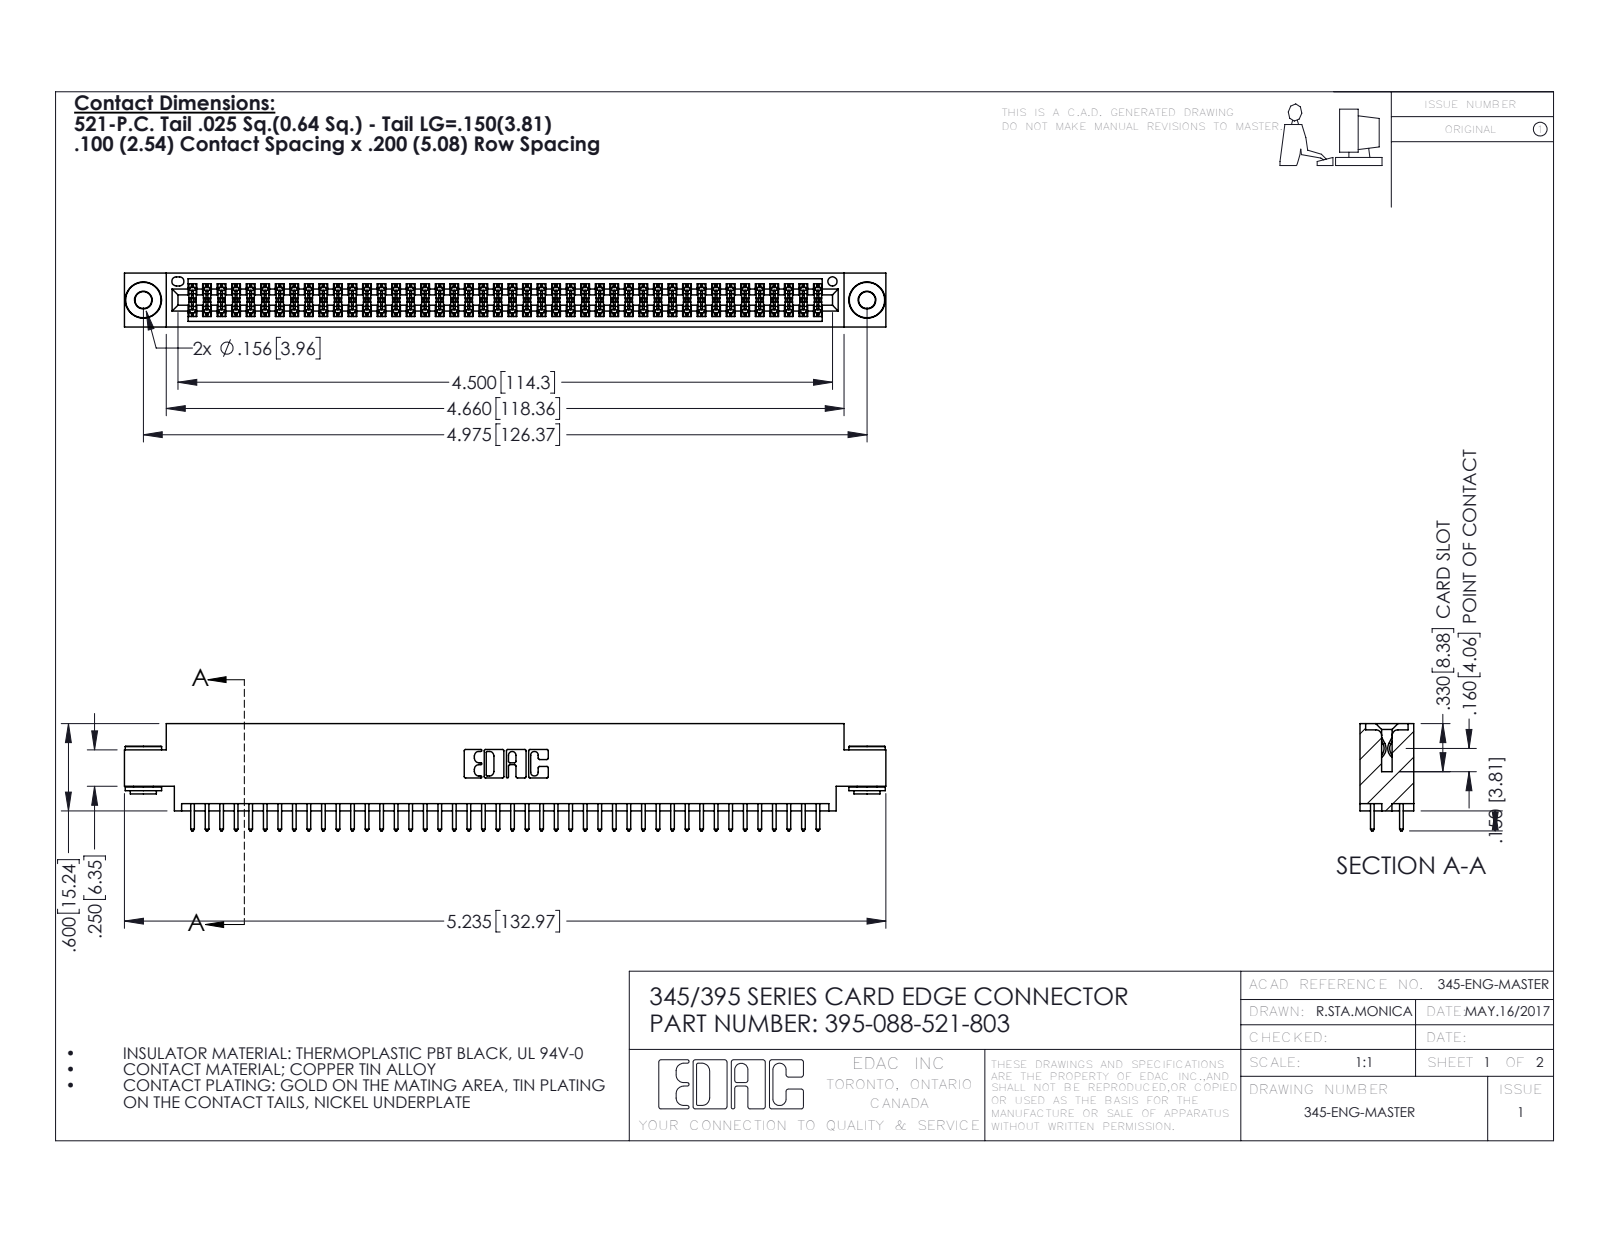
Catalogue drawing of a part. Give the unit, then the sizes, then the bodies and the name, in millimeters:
Units: millimetres
Overall size (bounding box): 133 × 18.7 × 9.4
Round holes (diameter × count): ⌀2.9 ×2, ⌀4 ×2, ⌀1.6 ×1
Round bosses / shafts (diameter × count): ⌀6.4 ×2, ⌀4.6 ×2, ⌀3.5 ×2
Partial cylindrical surfaces — rounded edges, fillets, slot ends (radius × count): R0.2 ×132, R0.3 ×88, R0.3 ×22, R0.2 ×6, R0.8 ×6, R0.7 ×3, R0.4 ×2, R0.5 ×2
Main face-to-face distances: 1.8, 7.6, 9.4, 5.1, 2.5, 6.9, 0.6, 5.7, 4.4, 3.8
Hole centre spacings: 6.9, 120.4, 126.4
Volume: 12 800 mm³ · Surface area: 19 080 mm²
Bodies: 91 solids, 4568 faces (2998 planar, 1562 cylindrical, 8 other)
Part name (STEP PRODUCT): 345-292-001_345-293-121; 395-088-521-803; 345 Part_0.170 Offset - 0.156 Dia-TH; 345-250-002_345-250-002-102
STEP written by: SolidWorks 2016 (CONFIG_CONTROL_DESIGN)
